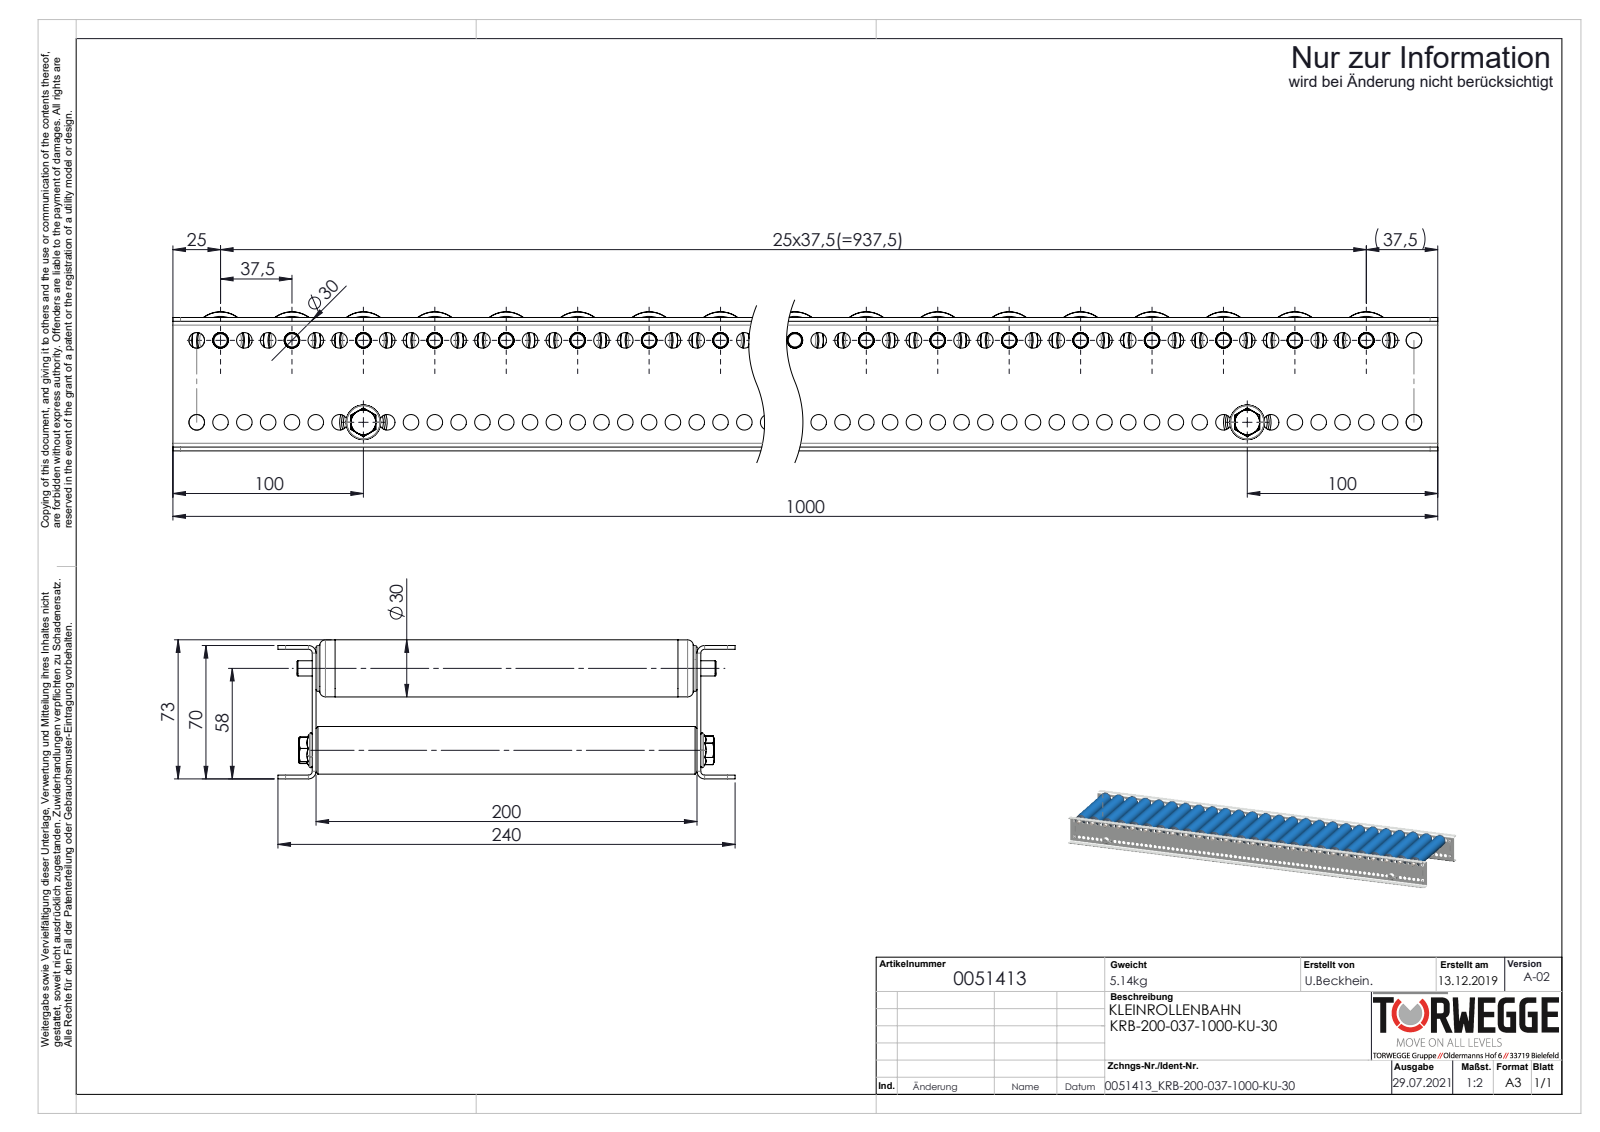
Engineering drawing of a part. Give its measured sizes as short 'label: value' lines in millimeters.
name: 0051413; S100995_TYP-KUT50-30x1,8-A8; S100994_Sperrzahnschraube_M08x16-8.8-A2K; 0017013_Tragrollenrohr-Ø30x1,8KU_KFG_L=180 (+4 more)
written by: SolidWorks 2020 (AUTOMOTIVE_DESIGN)
unit: mm
bodies: 64 solids, 6268 faces (1940 planar, 2352 cylindrical, 1976 other)
size: 1000 × 240 × 73
volume: 1 499 000 mm³; area: 1 762 000 mm²
holes: 158× ⌀8.2, 26× ⌀8.1, 26× ⌀22.6, 26× ⌀25.2, 2× ⌀6.8, 2× ⌀21
bosses: 28× ⌀8, 26× ⌀30, 26× ⌀29.9, 26× ⌀26.5, 26× ⌀26.4, 26× ⌀24, 2× ⌀25
rounds: 26× R5.05, 8× R4, 4× R2
face distances: 2, 202, 68, 200, 204, 66, 70, 10, 190, 12
hole spacings: 12.5, 25, 37.5, 50, 62.5, 75, 87.5, 100
